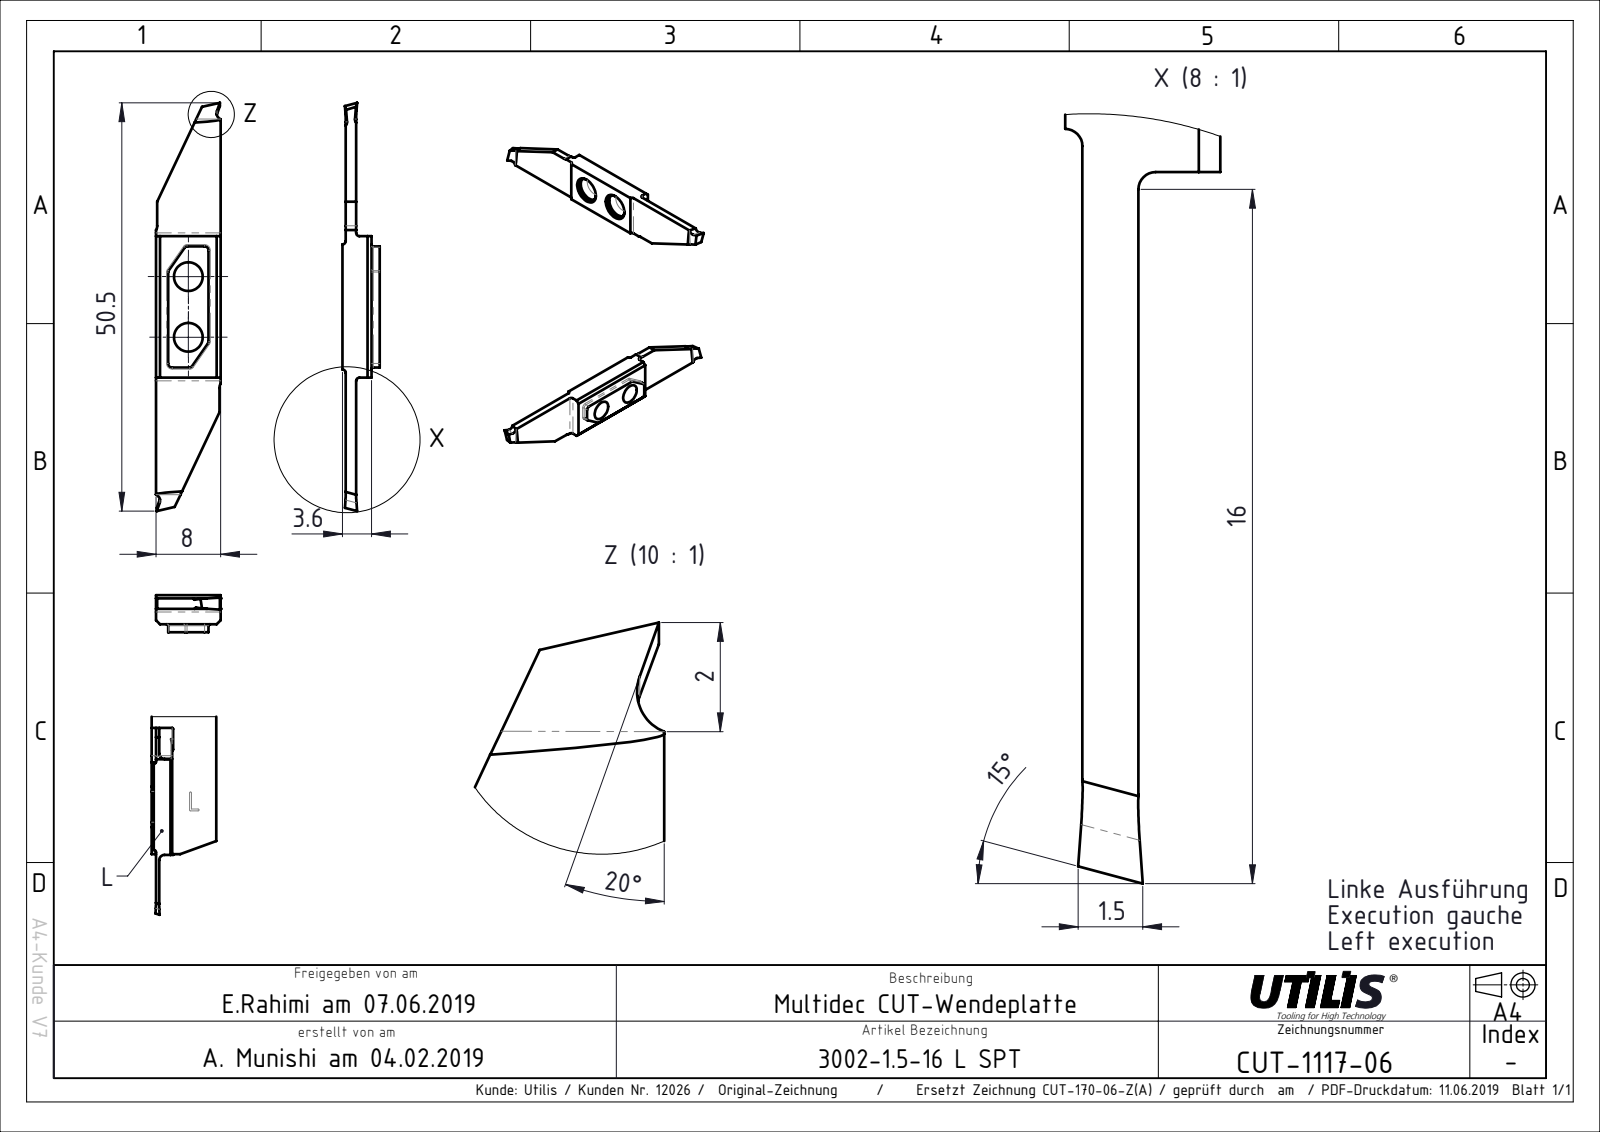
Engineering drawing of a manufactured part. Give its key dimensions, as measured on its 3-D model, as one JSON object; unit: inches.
{"part_name": "CUT-1117; ASME Y14.5", "step_written_by": "FormatWorks Professional (AP242_MANAGED_MODEL_BASED_3D_ENGINEERING_MIM_LF)", "units": "inches", "bodies": {"solids": 1, "faces": 34, "planar": 24, "cylindrical": 10, "other": 0}, "overall_size": [1.988, 0.315, 0.142], "volume_in3": 0.041, "surface_area_in2": 1.45, "round_holes": [[0.14, 2]], "partial_cylinders_radius": [[0.016, 4], [0.039, 2]], "face_to_face_distances": [0.05, 0.016, 0.067, 0.142, 0.126, 0.075, 0.315, 0.712, 0.689, 0.309], "hole_center_spacings": [0.295]}
